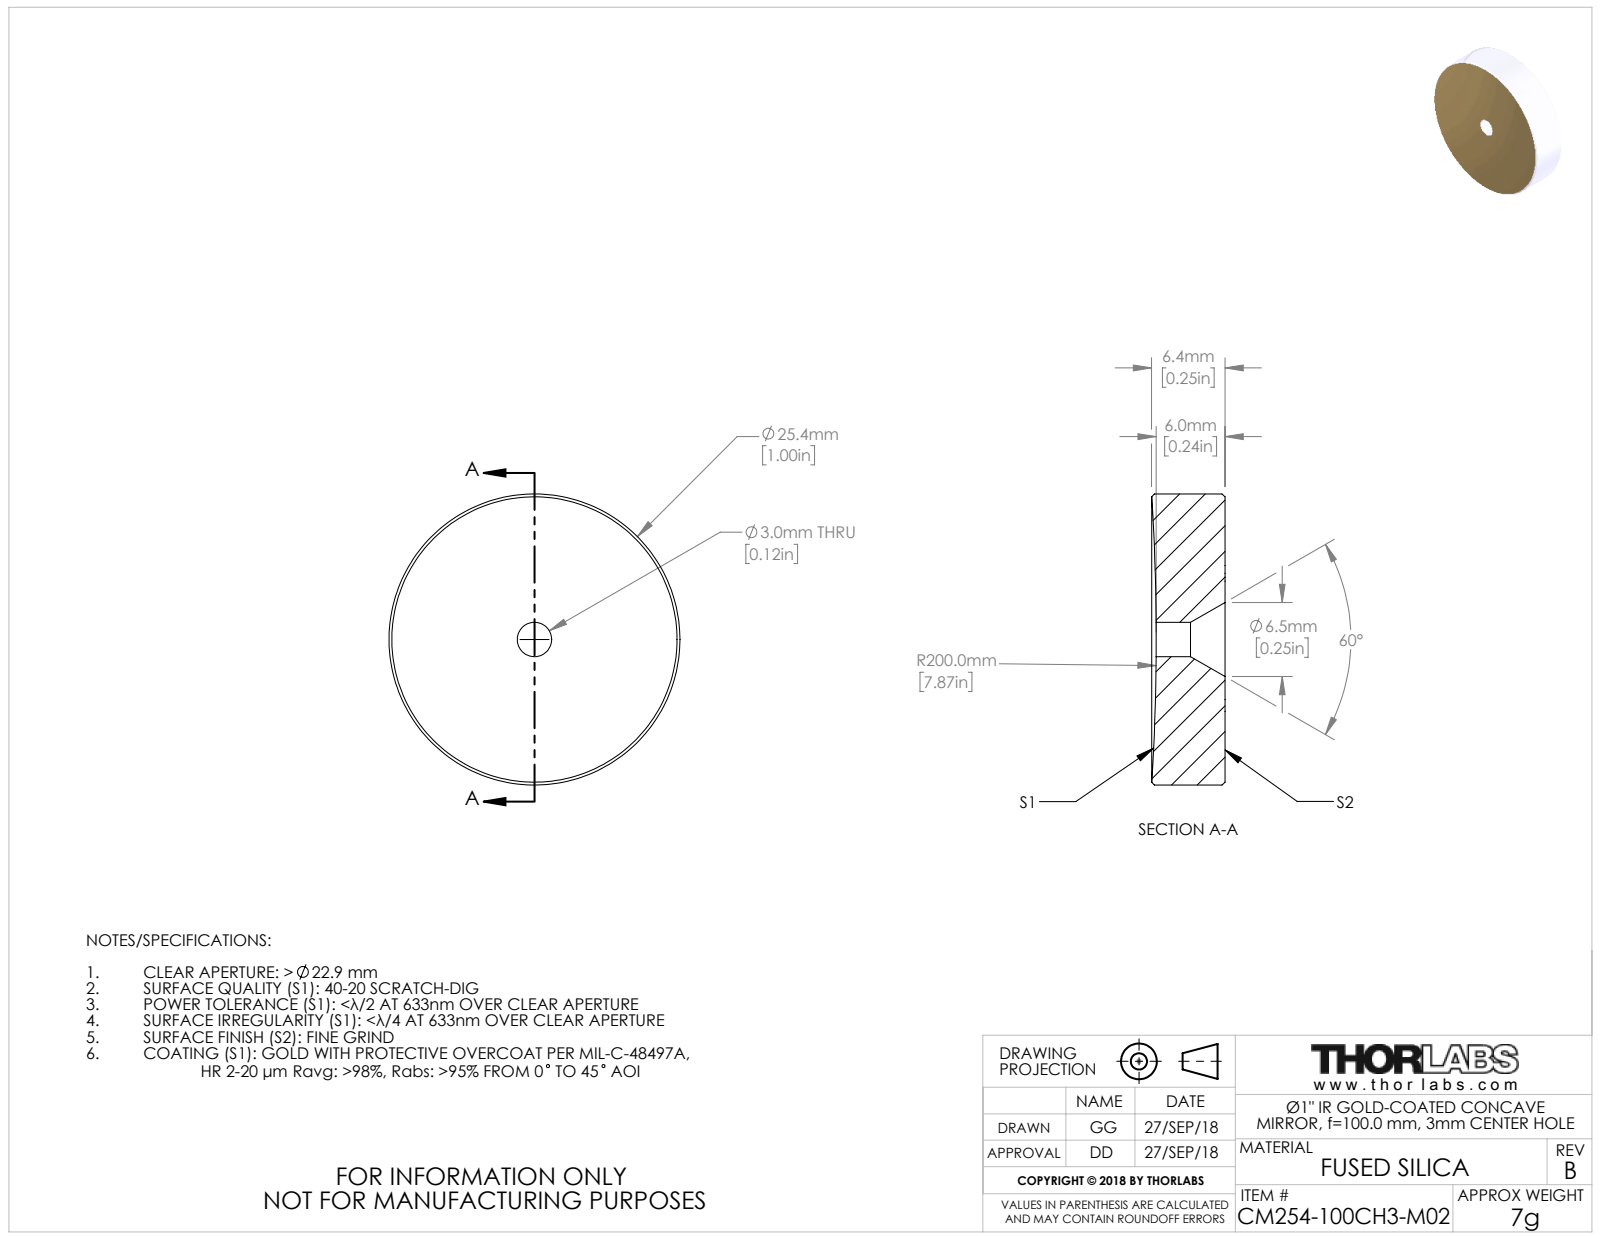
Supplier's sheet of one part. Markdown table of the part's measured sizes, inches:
| quantity | value |
| --- | --- |
| part name | TTN028022-E0W |
| STEP written by | SolidWorks 2014 (CONFIG_CONTROL_DESIGN) |
| units | inches |
| bodies | 1 solid, 46 faces (34 planar, 4 cylindrical, 8 other) |
| overall size | 1 × 1 × 0.251 |
| volume | 0.187 in³ |
| surface area | 2.388 in² |
| round holes (diameter × count) | 0.118 × 1 |
| round bosses / shafts (diameter × count) | 1 × 1 |
